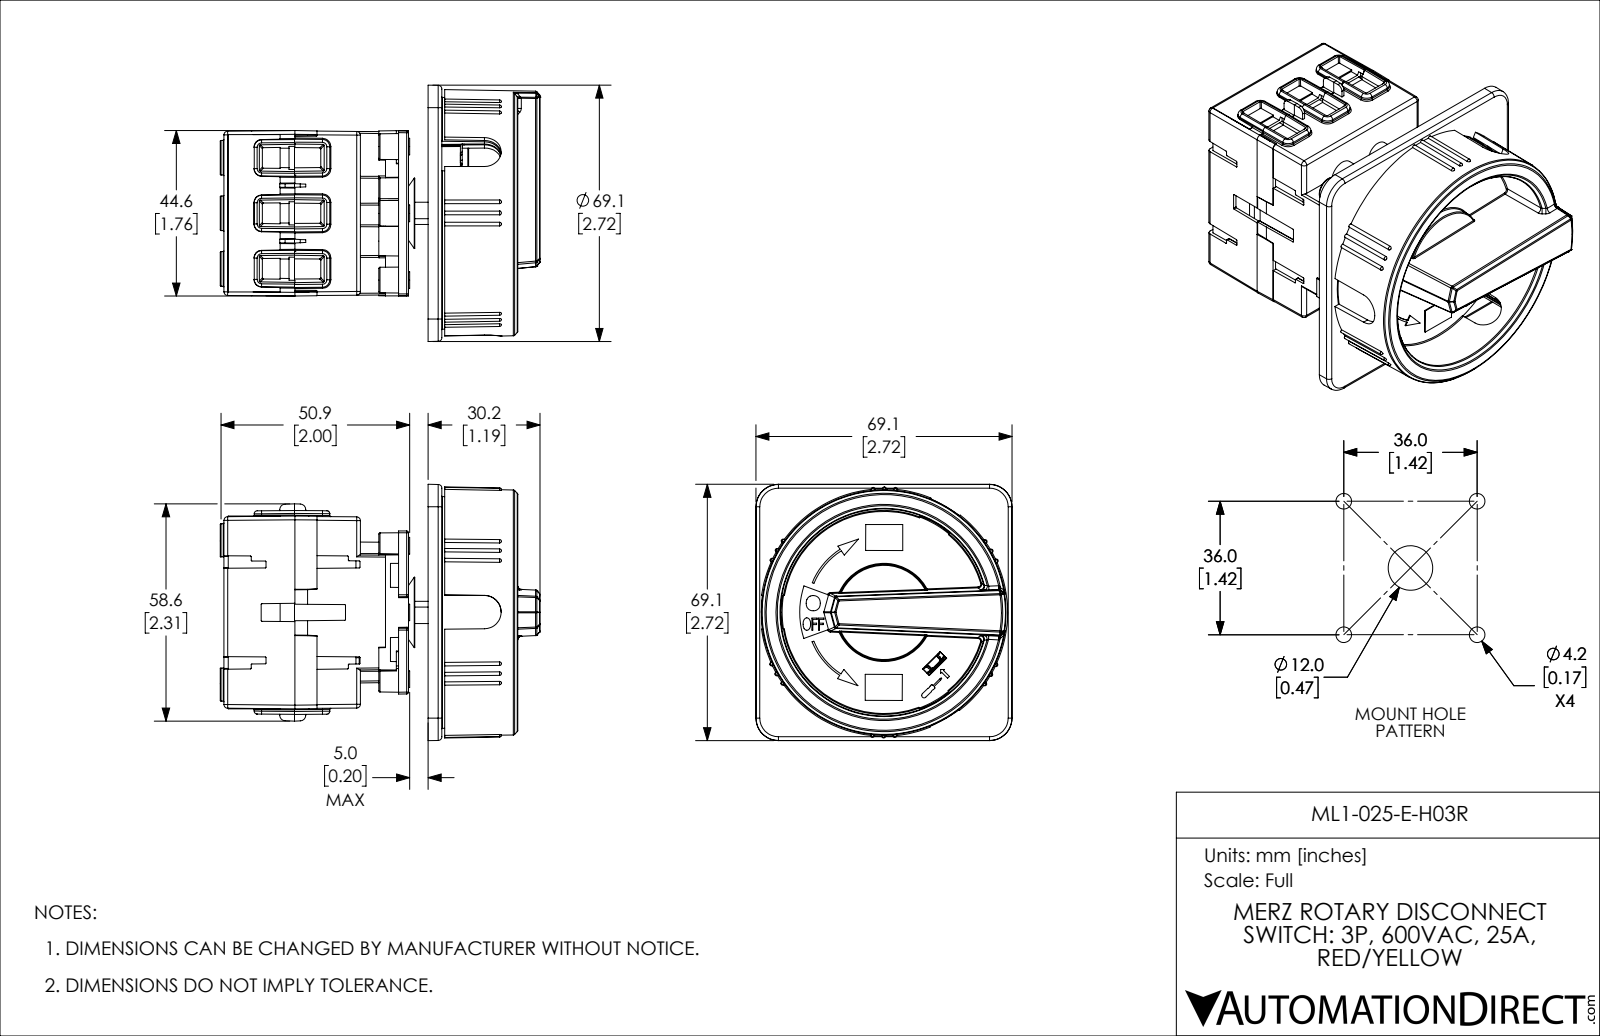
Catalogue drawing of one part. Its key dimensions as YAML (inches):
part_name: "ML1-025-E-H03R"
step_written_by: "SolidWorks 2019 (AUTOMOTIVE_DESIGN)"
units: inches
bodies: {solids: 1, faces: 2964, planar: 1185, cylindrical: 610, other: 1169}
overall_size: [3.398, 2.722, 2.722]
volume: 8.361
surface_area: 101.4
round_bosses_or_shafts:
  - {diameter: 0.071, count: 2}
  - {diameter: 0.748, count: 1}
  - {diameter: 0.236, count: 1}
partial_cylinders:
  - {radius: 0.02, count: 132}
  - {radius: 0.012, count: 68}
  - {radius: 0.039, count: 50}
  - {radius: 0.008, count: 44}
  - {radius: 0.008, count: 41}
  - {radius: 0.01, count: 39}
  - {radius: 0.031, count: 34}
  - {radius: 0.079, count: 12}
face_to_face_distances: [0.059, 0.138, 0.197, 0.079, 0.276, 0.571, 0.02, 0.551, 0.295, 0.807]
